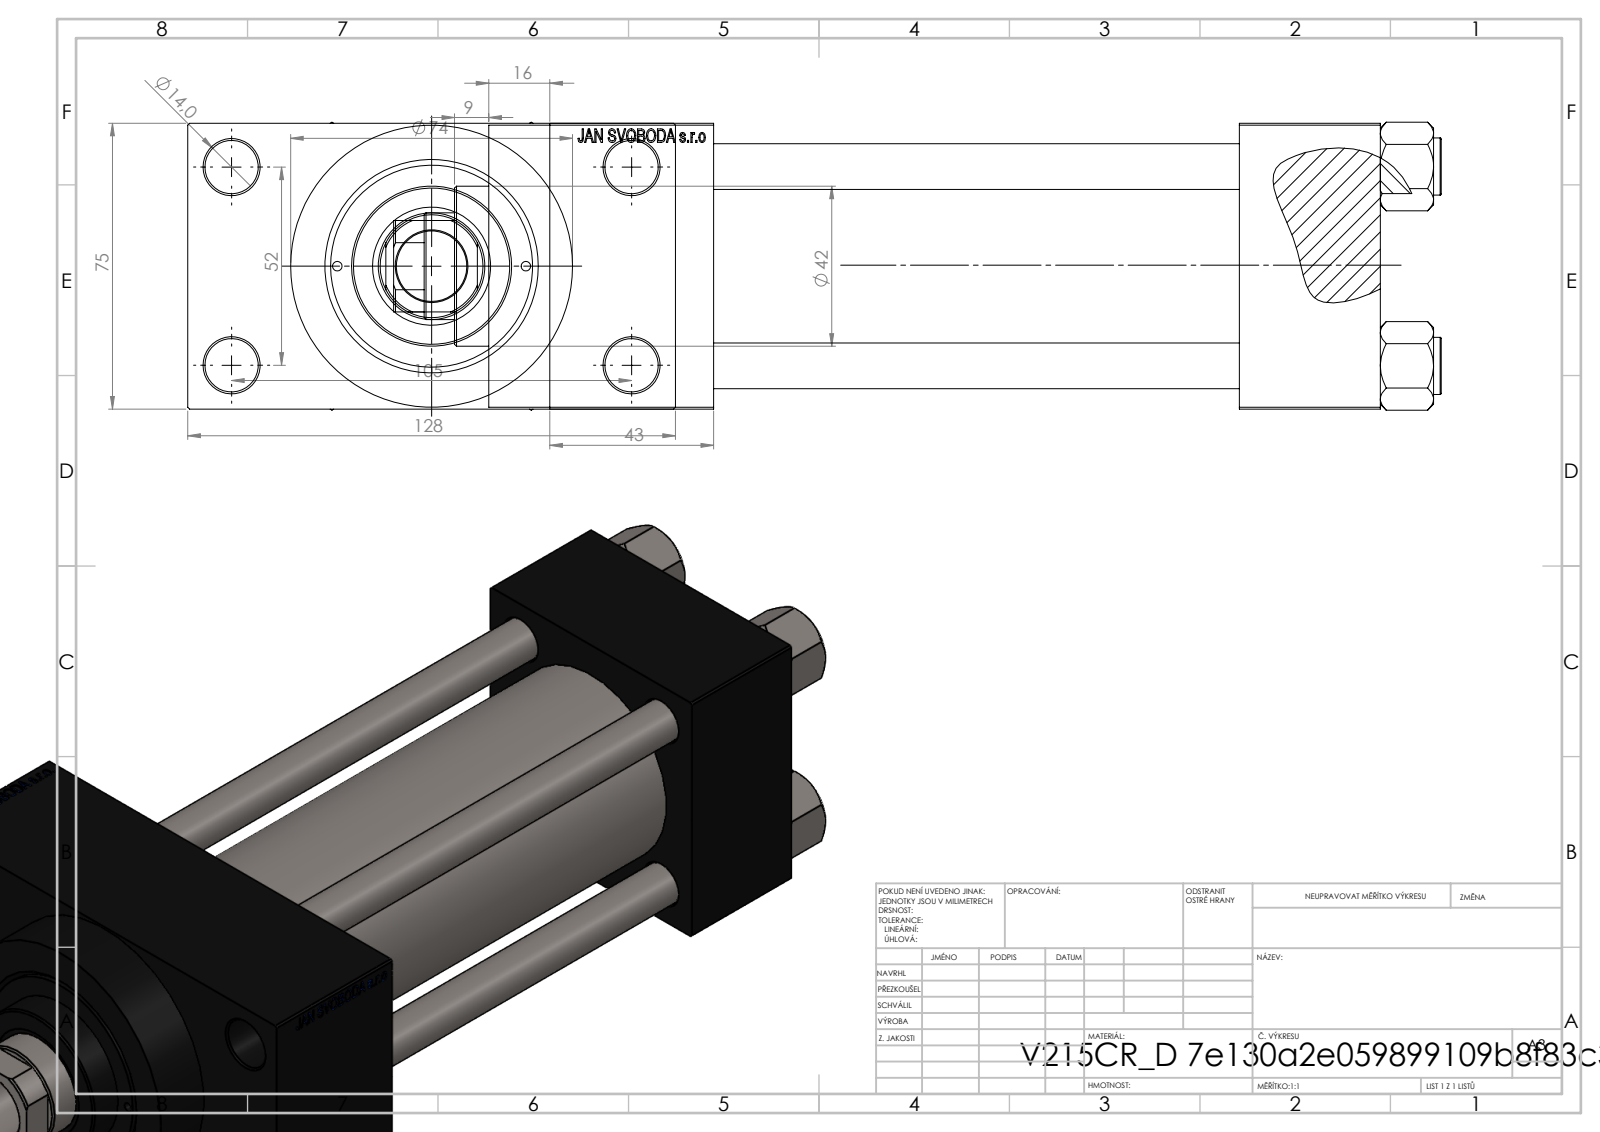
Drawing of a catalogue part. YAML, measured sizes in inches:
part_name: "V215CR_VCP_D; V215_VC_A; NUT_M5_D; V215CR_D_Body (+1 more)"
step_written_by: "SolidWorks 2019 (CONFIG_CONTROL_DESIGN)"
units: inches
bodies: {solids: 11, faces: 1111, planar: 499, cylindrical: 92, other: 520}
overall_size: [10.827, 5.039, 2.974]
volume: 56.84
surface_area: 335.2
round_holes:
  - {diameter: 0.472, count: 4}
  - {diameter: 0.551, count: 4}
  - {diameter: 0.098, count: 2}
  - {diameter: 0.276, count: 2}
  - {diameter: 0.825, count: 2}
  - {diameter: 1.181, count: 2}
  - {diameter: 0.728, count: 1}
  - {diameter: 1.102, count: 1}
  - {diameter: 1.22, count: 1}
  - {diameter: 1.614, count: 1}
  - {diameter: 1.969, count: 1}
  - {diameter: 2.087, count: 1}
round_bosses_or_shafts:
  - {diameter: 0.591, count: 4}
  - {diameter: 2.913, count: 1}
  - {diameter: 2.205, count: 1}
  - {diameter: 1.654, count: 1}
partial_cylinders:
  - {radius: 0.531, count: 1}
face_to_face_distances: [2.953, 5.433, 1.457, 6.89, 1.043, 8.583, 7.126, 1.693, 3.996, 0.63]
hole_center_spacings: [1.031, 1.037, 1.456, 1.497, 2.059, 2.253, 2.3, 2.307]
